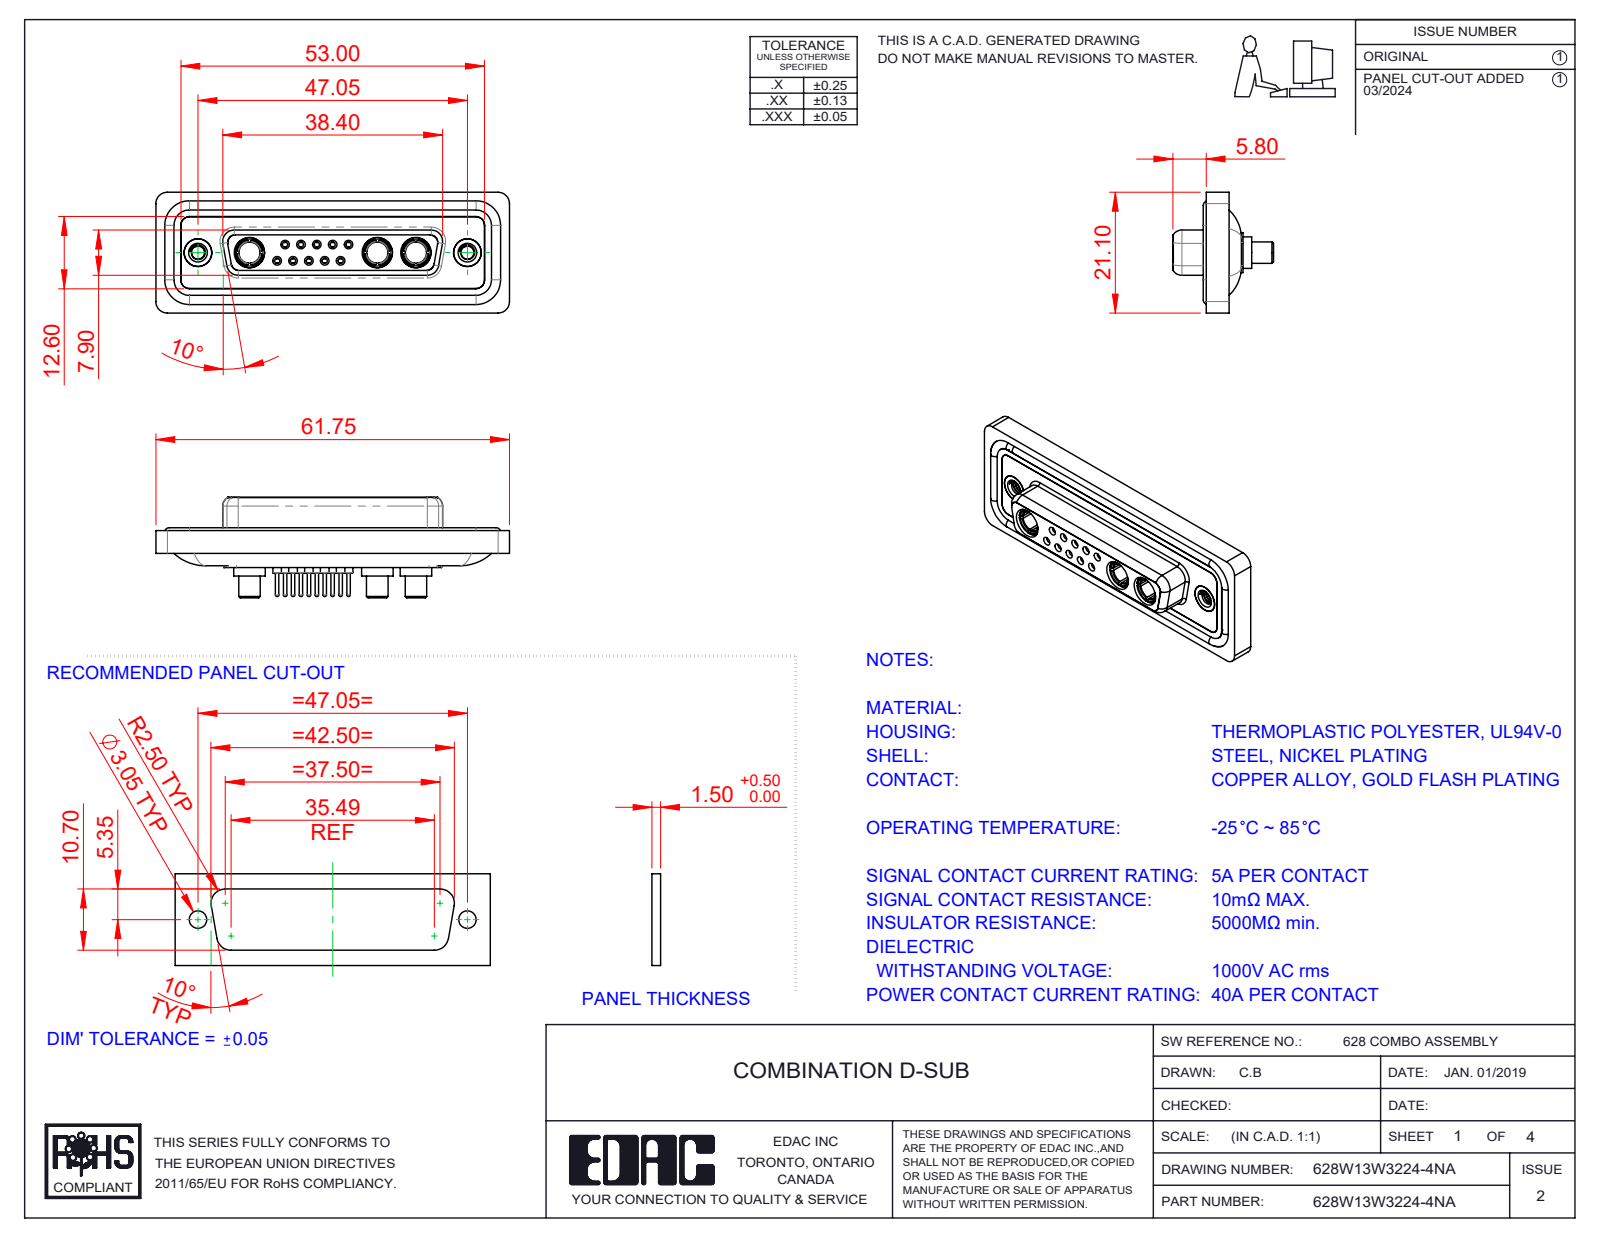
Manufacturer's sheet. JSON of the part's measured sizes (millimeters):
{"part_name": "628Combo Threaded Rivet_A; 628Combo Contact Row 1_24; 628W13W3224-4NA; 628Combo Contact Row 2_24 (+5 more)", "step_written_by": "SolidWorks 2023 (CONFIG_CONTROL_DESIGN)", "units": "millimeters", "bodies": {"solids": 23, "faces": 1156, "planar": 342, "cylindrical": 449, "other": 365}, "overall_size": [61.75, 21.1, 17.55], "volume_mm3": 8330, "surface_area_mm2": 13739, "round_holes": [[0.9, 10], [1.1, 10], [1.5, 10], [2, 10], [1.6, 5], [1.7, 5], [4.85, 5], [3.7, 3], [5.3, 3], [2.26, 2], [4, 2], [4.05, 2]], "round_bosses_or_shafts": [[2.2, 10], [0.6, 10], [1.6, 9], [5.5, 3], [5.2, 3], [4.96, 3], [4.75, 3], [3.75, 3]], "partial_cylinders_radius": [[1.5, 22], [2, 18], [1.35, 8], [1.6, 8], [0.25, 4], [0.5, 4], [0.6, 4], [0.65, 4]], "face_to_face_distances": [0.4, 1.8, 7.45, 5.65, 0.5, 6.6, 7.05, 1.6, 2.9, 1.1], "hole_center_spacings": [3.16, 2.77, 5.03, 5.04, 5.54, 8.31, 7.49, 2.76]}
